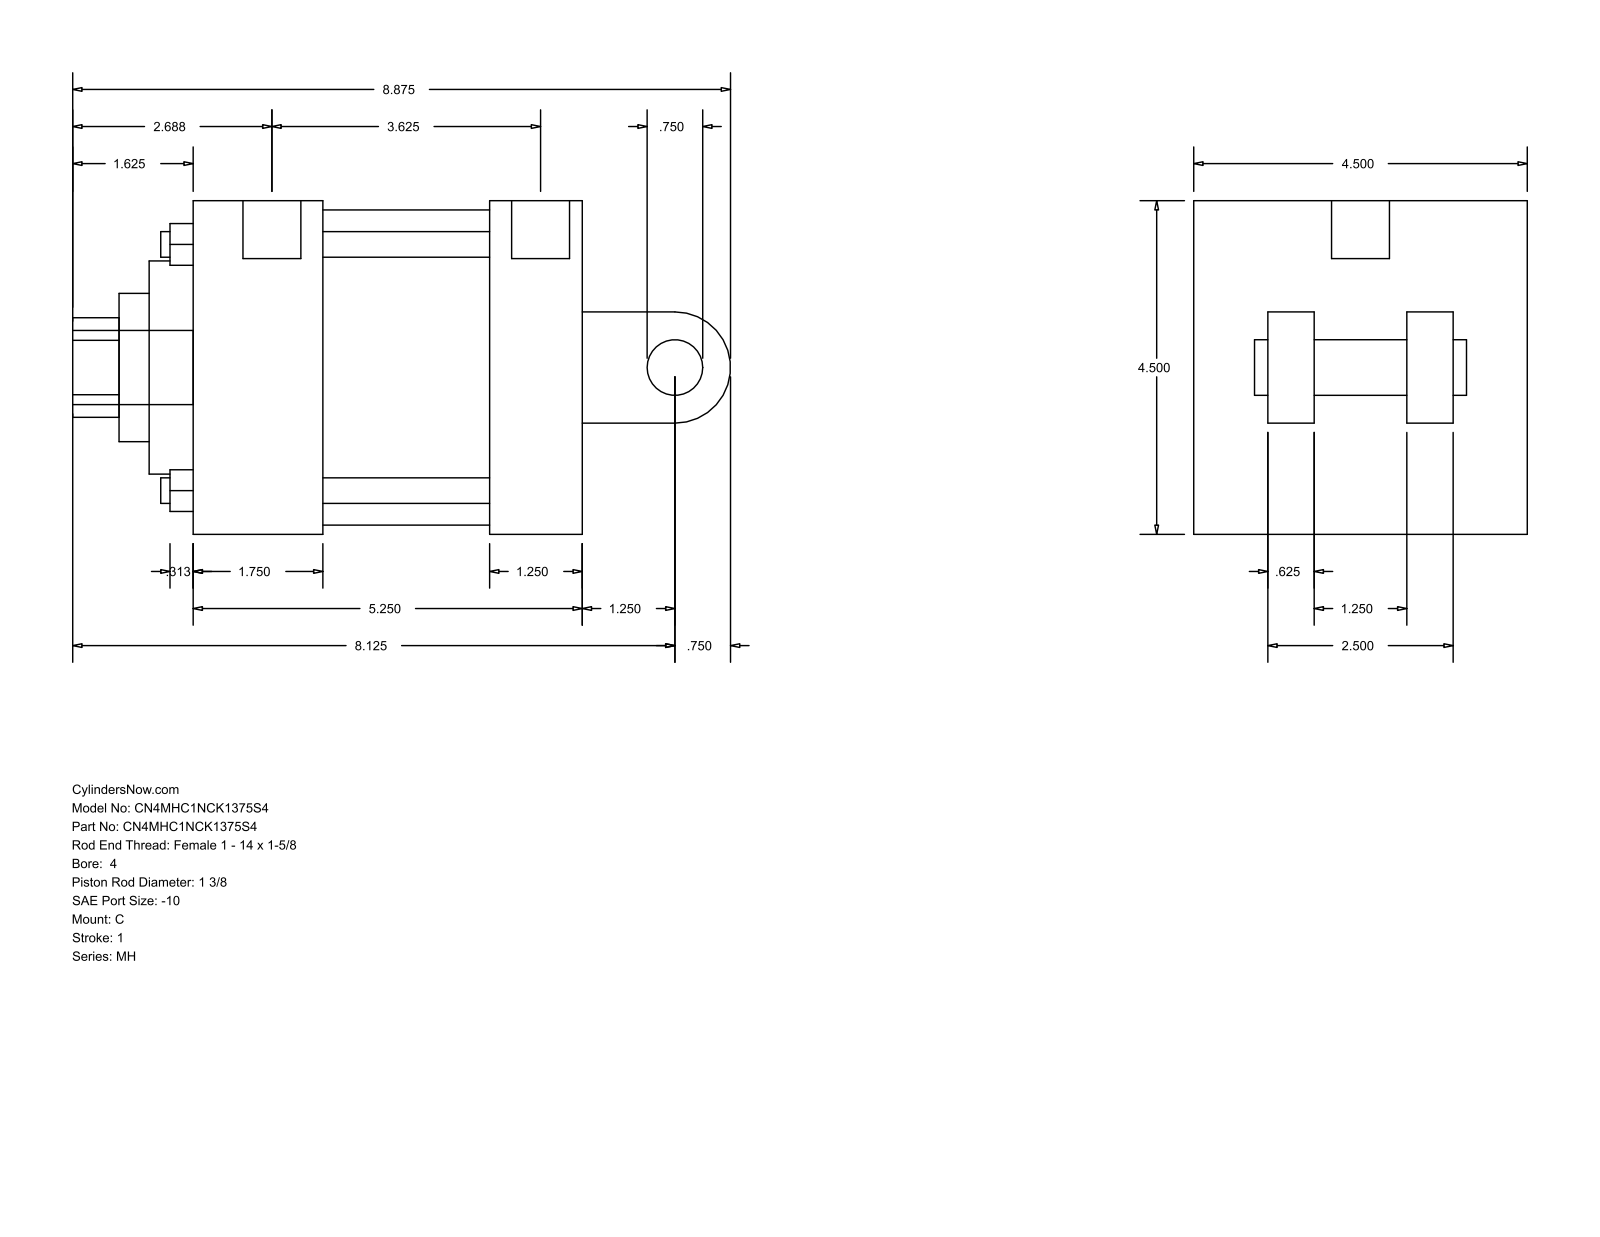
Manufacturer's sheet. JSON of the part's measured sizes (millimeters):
{"part_name": "MH_C__0400_1.375", "step_written_by": "GSSL Pune (CONFIG_CONTROL_DESIGN)", "units": "millimeters", "bodies": {"solids": 0, "faces": 101, "planar": 71, "cylindrical": 30, "other": 0}, "overall_size": [225.43, 114.3, 114.3], "round_holes": [[8.76, 4], [8.73, 2], [19.84, 1], [34.92, 1], [50.8, 1], [73.03, 1], [107.95, 1]], "round_bosses_or_shafts": [[8.73, 2], [25.4, 1], [19.84, 1], [19.05, 1]], "partial_cylinders_radius": [[17.06, 1], [19.05, 1]], "face_to_face_distances": [114.3, 133.35, 88.9, 44.45, 101.61, 57.16, 31.74, 73.03, 41.27, 38.1], "hole_center_spacings": [59.62, 84.32, 119.25, 1.59]}
